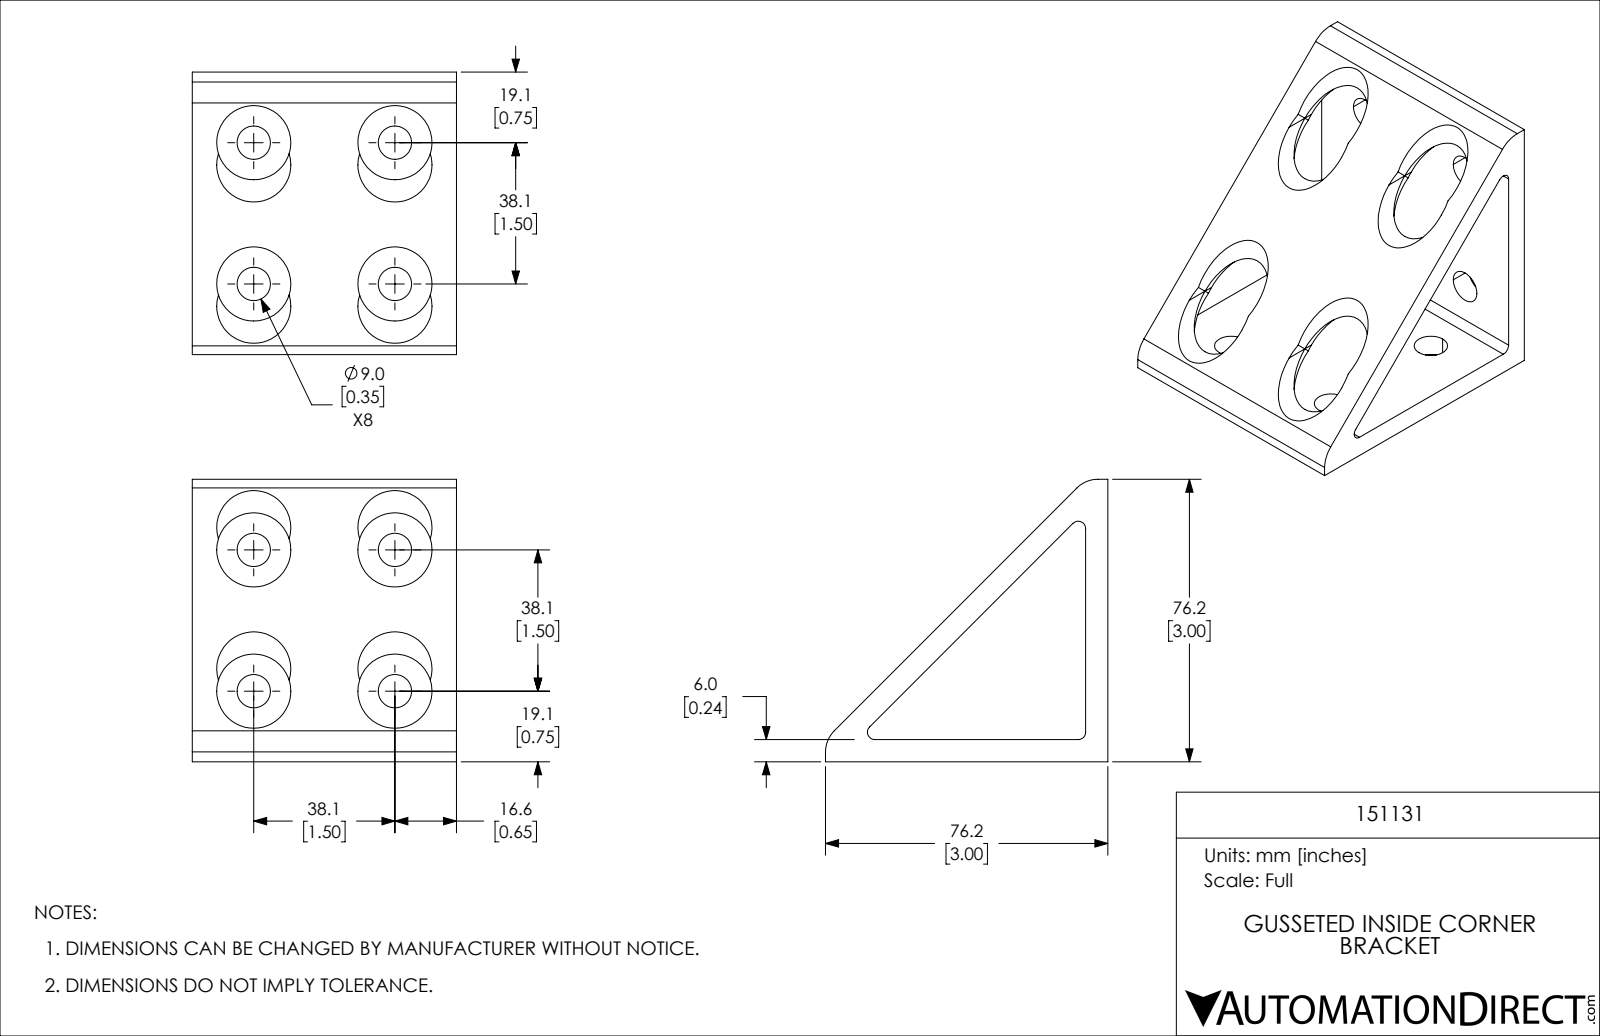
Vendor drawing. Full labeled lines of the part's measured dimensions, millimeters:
Part name (STEP PRODUCT): 151131
STEP written by: SolidWorks 2021 (CONFIG_CONTROL_DESIGN)
Units: millimetres
Bodies: 1 solid, 74 faces (10 planar, 64 cylindrical, 0 other)
Overall size (bounding box): 76.2 × 76.2 × 71.3
Volume: 87 455 mm³ · Surface area: 34 201 mm²
Round holes (diameter × count): ⌀9 ×8, ⌀20 ×8
Partial cylindrical surfaces — rounded edges, fillets, slot ends (radius × count): R2 ×3, R8 ×2
Main face-to-face distances: 6, 71.3, 76.2, 70.2
Hole centre spacings: 38.1, 53.88
